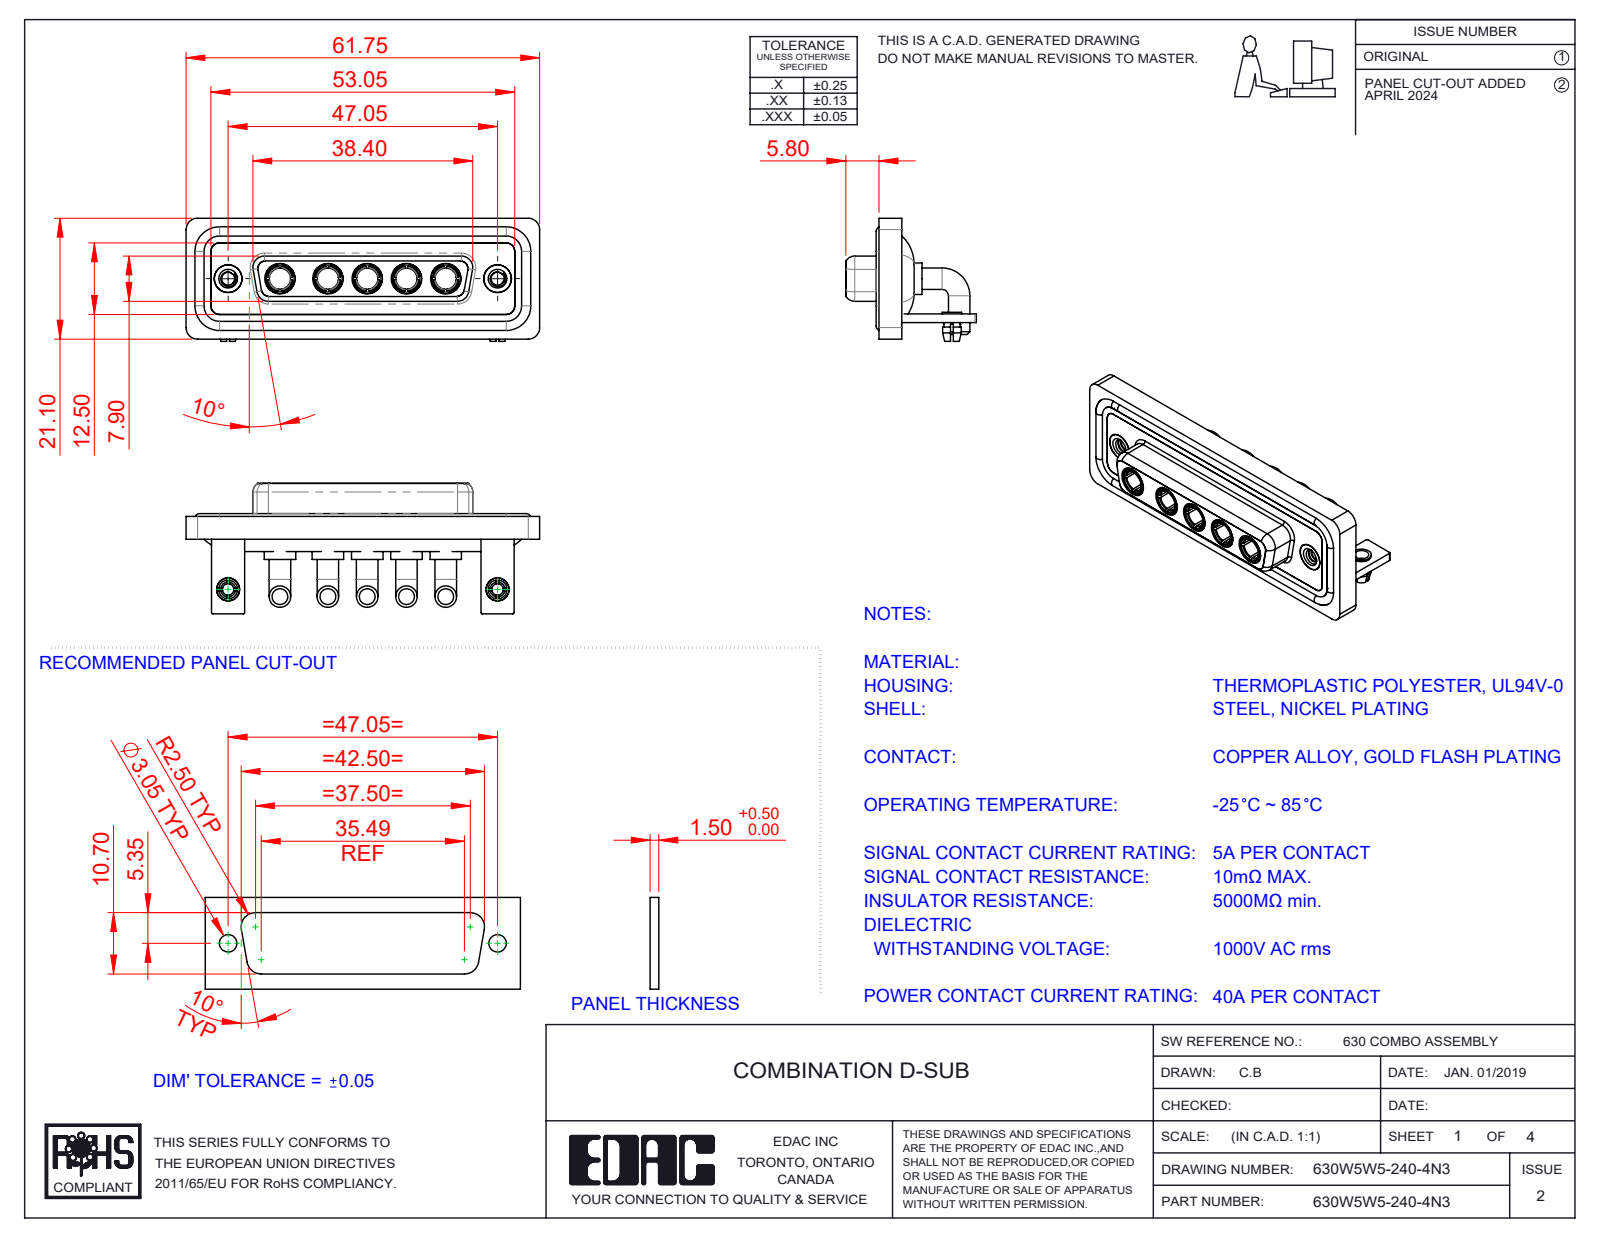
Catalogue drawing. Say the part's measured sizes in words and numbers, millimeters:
The part is named "630Combo Board Lock_50 Contacts; 630Combo Shell Front_25 Contacts; 630Combo Shell Rear_25 Contacts; 630Combo Threaded Rivet_2 (+5 more)". Its 3-D file was written by "SolidWorks 2023 (CONFIG_CONTROL_DESIGN)". It is 21 solids with 916 faces: 318 planar, 369 cylindrical and 229 other. Overall it measures 61.75 by 22.8 by 21.5 millimeters. Its volume is 9 201 cubic millimeters and its surface area 14 978 square millimeters. Round holes: 7 of diameter 4.85, 5 of diameter 3.7, 5 of diameter 5.3, 2 of diameter 2, 2 of diameter 2.26, 2 of diameter 2.5, 2 of diameter 3.2, 2 of diameter 4, 2 of diameter 4.05, 2 of diameter 5. Round bosses or shafts: 10 of diameter 3.75, 5 of diameter 5.5, 5 of diameter 5.2, 5 of diameter 4.96, 5 of diameter 4.75, 4 of diameter 1.6, 2 of diameter 4.95, 2 of diameter 4.8. Partial cylindrical surfaces (rounded edges, fillets, slot ends): 19 of radius 2, 18 of radius 1.5, 16 of radius 0.25, 8 of radius 1.35, 8 of radius 1.6, 5 of radius 0.5, 5 of radius 2.1, 4 of radius 0.6. The main face-to-face distances are 0.4, 1.8, 2.9, 3.7, 1.5, 4.1, 1.1, 1.4, 1.6, 2.5. The hole center spacings are 6.86, 9.04, 38.01, 47.05, 6.87, 8.38, 13.72, 13.73.
